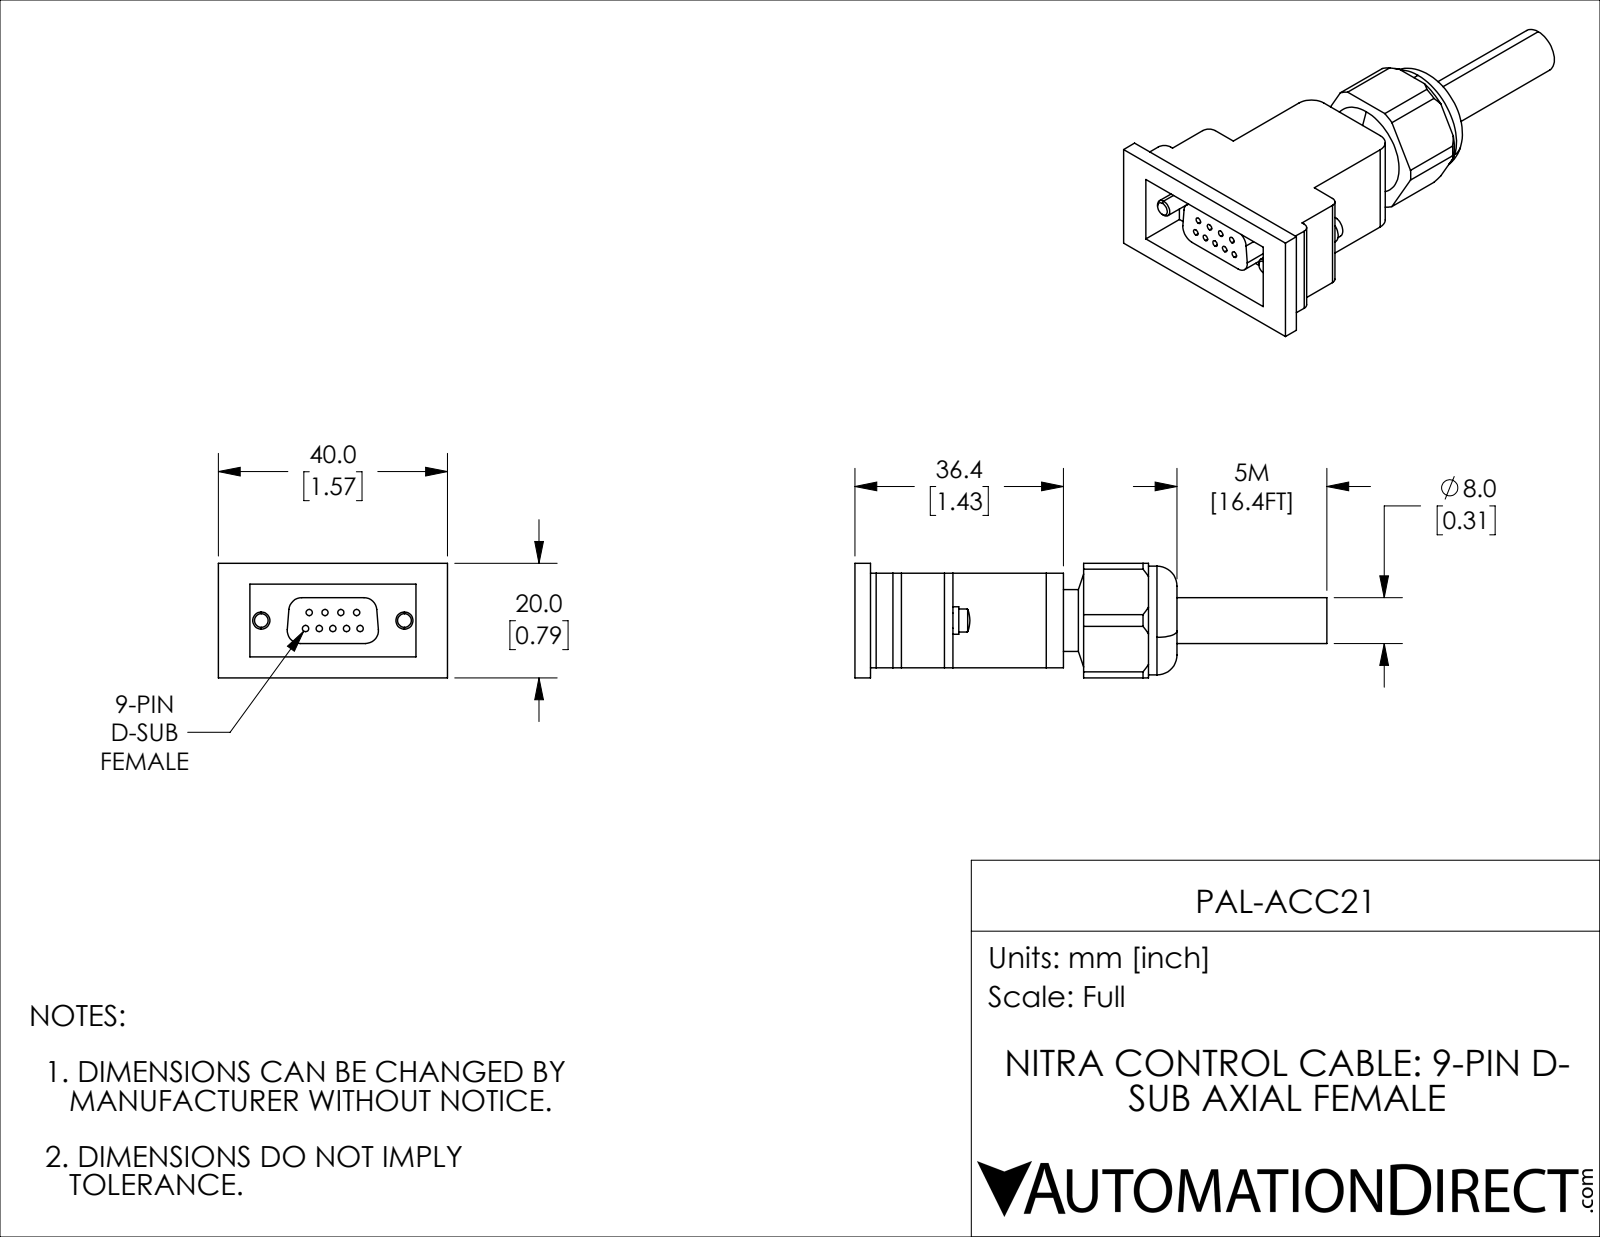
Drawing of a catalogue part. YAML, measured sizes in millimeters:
part_name: "PAL-ACC21"
step_written_by: "SolidWorks 2019 (CONFIG_CONTROL_DESIGN)"
units: millimeters
bodies: {solids: 1, faces: 139, planar: 61, cylindrical: 56, other: 22}
overall_size: [82.4, 40, 20]
volume: 20838
surface_area: 8406
round_holes:
  - {diameter: 1.1, count: 9}
  - {diameter: 10.6, count: 1}
round_bosses_or_shafts:
  - {diameter: 4.8, count: 2}
  - {diameter: 4, count: 2}
  - {diameter: 3, count: 2}
  - {diameter: 19, count: 1}
  - {diameter: 10.8, count: 1}
  - {diameter: 8, count: 1}
partial_cylinders:
  - {radius: 1.5, count: 4}
  - {radius: 2.25, count: 4}
  - {radius: 1, count: 2}
  - {radius: 3, count: 2}
  - {radius: 11, count: 1}
face_to_face_distances: [16.5, 20, 1.9, 14.6, 1.75, 3.65, 16.35, 18.25, 6, 26]
hole_center_spacings: [2.76, 2.38, 4.76, 2.87, 4.38, 4.96, 5.52, 7.14]
